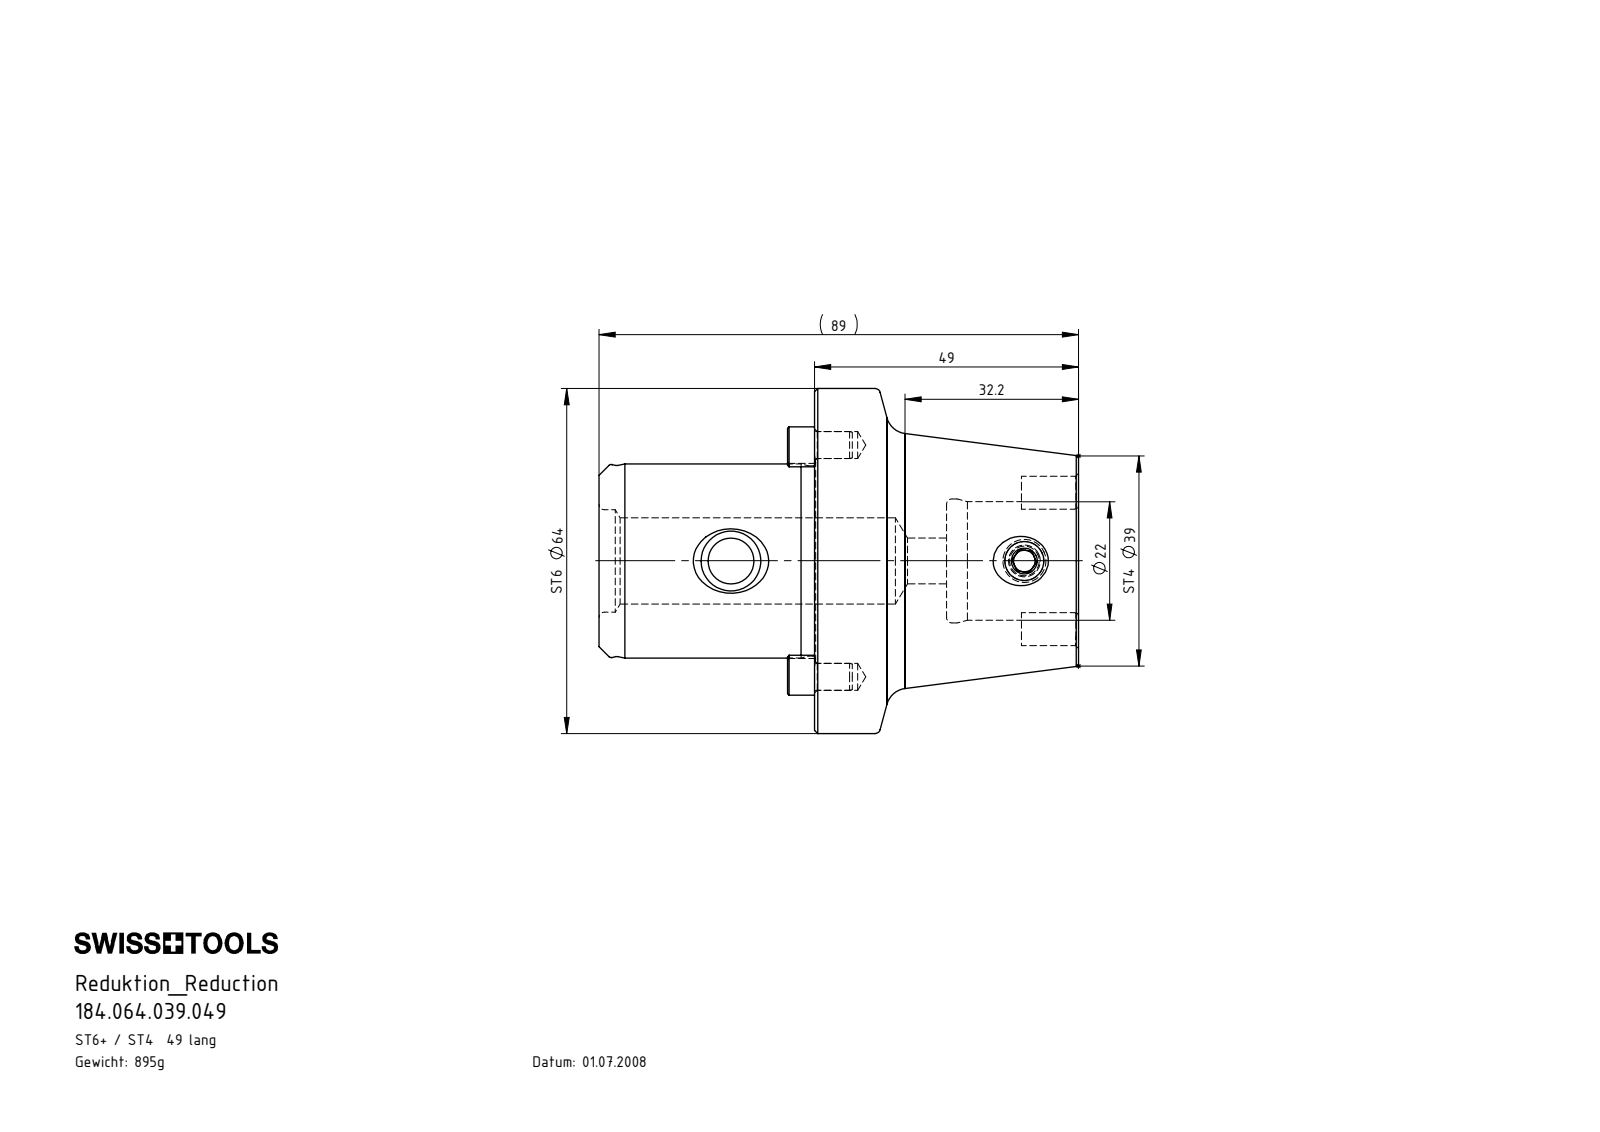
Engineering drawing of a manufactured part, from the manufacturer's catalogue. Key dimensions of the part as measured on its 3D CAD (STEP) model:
Part name (STEP PRODUCT): ST4-ER1.001.011_A; ST6-ER2.001.012_A; ST6-ST4.K01.049; ST6-ST4.K01.049_A
STEP written by: SolidWorks 2015 (CONFIG_CONTROL_DESIGN)
Units: millimetres
Bodies: 4 solids, 166 faces (26 planar, 47 cylindrical, 93 other)
Overall size (bounding box): 89 × 64 × 64
Volume: 114 109 mm³ · Surface area: 23 620 mm²
Round holes (diameter × count): ⌀5 ×2, ⌀8.5 ×2, ⌀7.25 ×1, ⌀16 ×1, ⌀19 ×1, ⌀22 ×1, ⌀23 ×1
Round bosses / shafts (diameter × count): ⌀64 ×1, ⌀36 ×1, ⌀35.8 ×1, ⌀35.3 ×1, ⌀8 ×1
Partial cylindrical surfaces — rounded edges, fillets, slot ends (radius × count): R0.5 ×4, R3.2 ×2, R5.47 ×2, R18.05 ×2
Main face-to-face distances: 49, 24.5, 40, 89, 64.5, 35, 5, 29.5, 54, 18.9
Hole centre spacings: 21.5, 43, 54.45
